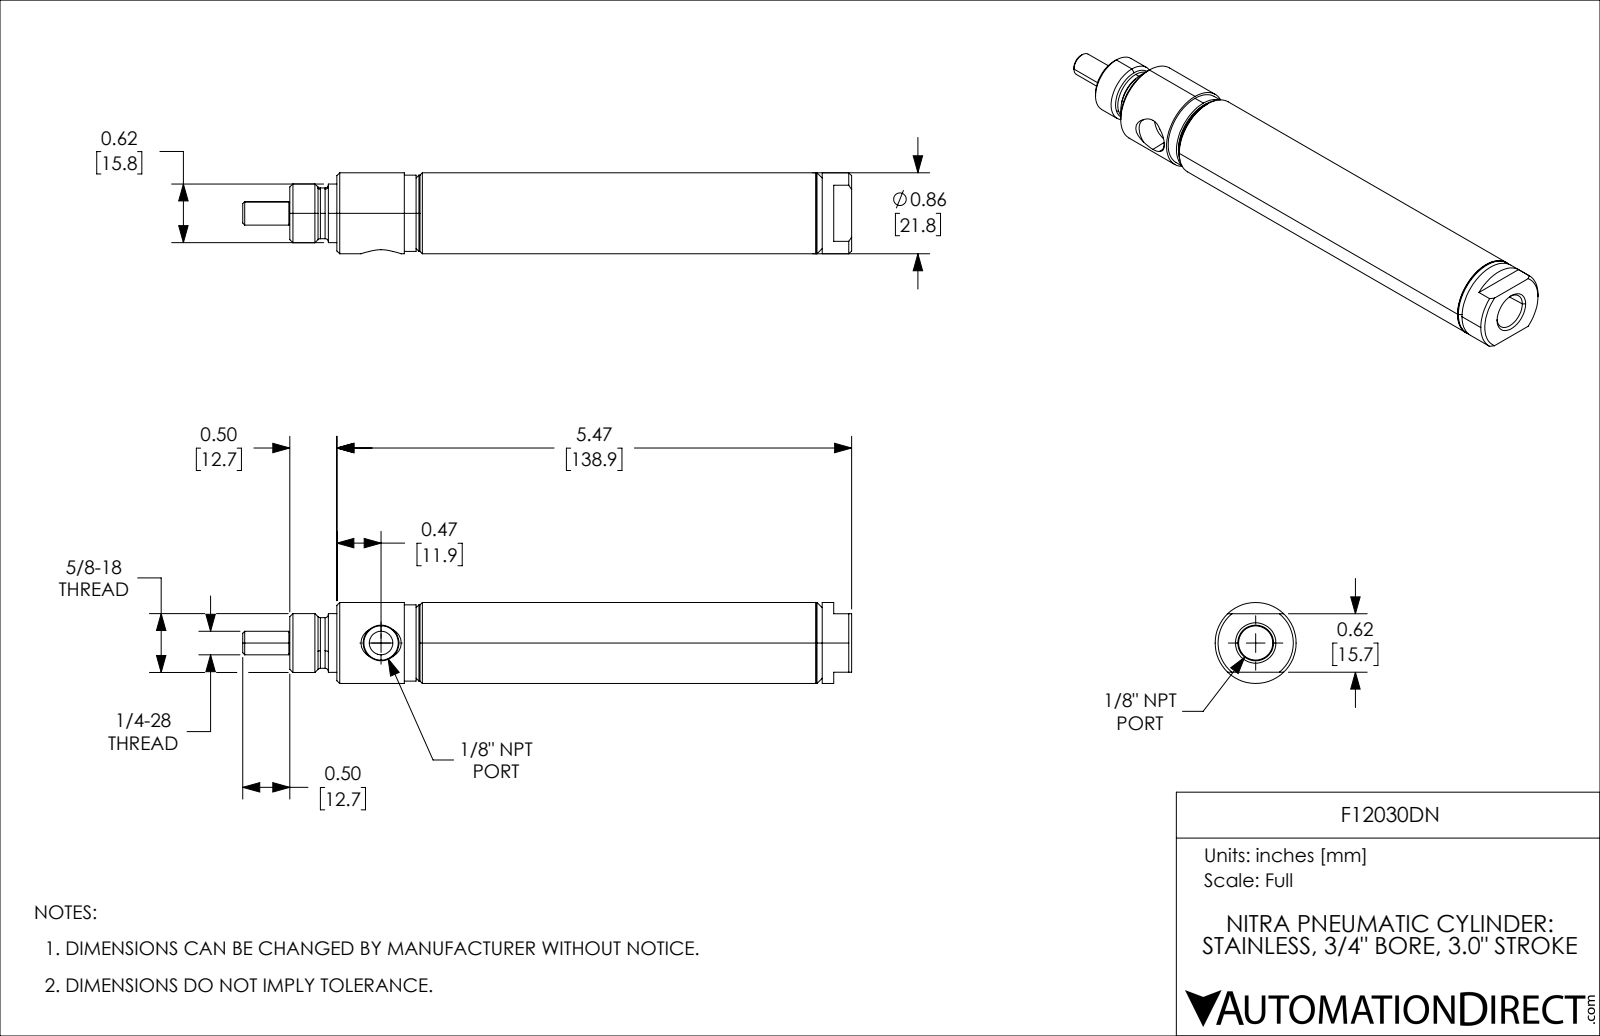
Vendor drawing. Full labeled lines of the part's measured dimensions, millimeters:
Part name (STEP PRODUCT): F12030DN; F12030DN_3; F12030DN_9; F12030DN_5 (+1 more)
STEP written by: SolidWorks 2021 (CONFIG_CONTROL_DESIGN)
Units: millimetres
Bodies: 4 solids, 124 faces (22 planar, 46 cylindrical, 56 other)
Overall size (bounding box): 164.31 × 21.84 × 21.84
Volume: 32 084 mm³ · Surface area: 25 306 mm²
Round holes (diameter × count): ⌀6.35 ×1, ⌀6.95 ×1, ⌀12.7 ×1, ⌀17.83 ×1
Round bosses / shafts (diameter × count): ⌀21.84 ×1, ⌀20.57 ×1, ⌀19.35 ×1, ⌀15.88 ×1, ⌀15.81 ×1, ⌀13.68 ×1, ⌀6.35 ×1, ⌀5.84 ×1
Main face-to-face distances: 21.43, 76.2, 97.63, 111.12, 34.92, 13.49, 12.7, 27.79, 103.99, 125.42
